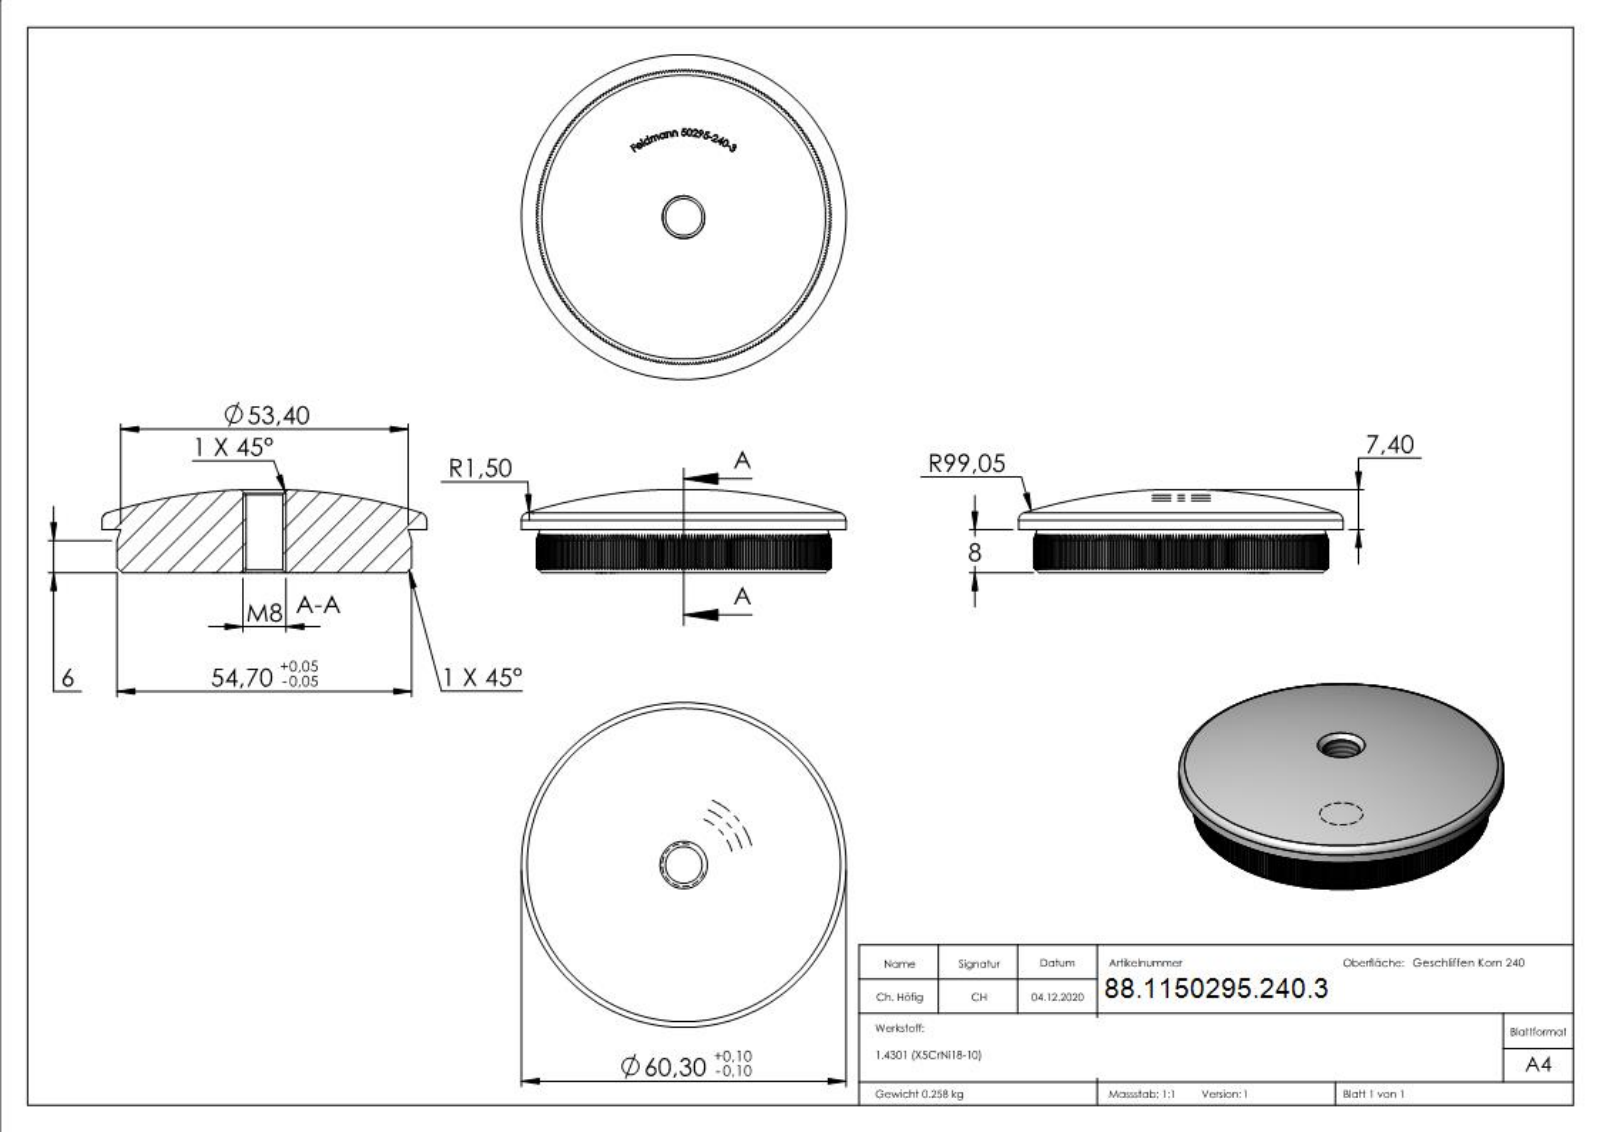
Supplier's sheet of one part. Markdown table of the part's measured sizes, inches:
| quantity | value |
| --- | --- |
| part name | 50295-240-3 |
| STEP written by | SolidWorks 2018 (CONFIG_CONTROL_DESIGN) |
| units | inches |
| bodies | 1 solid, 1136 faces (713 planar, 294 cylindrical, 129 other) |
| overall size | 2.374 × 2.374 × 0.606 |
| volume | 1.991 in³ |
| surface area | 13.26 in² |
| round holes (diameter × count) | 0.268 × 1 |
| round bosses / shafts (diameter × count) | 2.374 × 1 |
| partial cylindrical surfaces (radius × count) | 1.077 × 1 |
| main face-to-face distances | 0.315, 1.063, 1.062, 1.064, 1.065, 1.061, 0.311, 0.021, 0.52, 0.543 |
